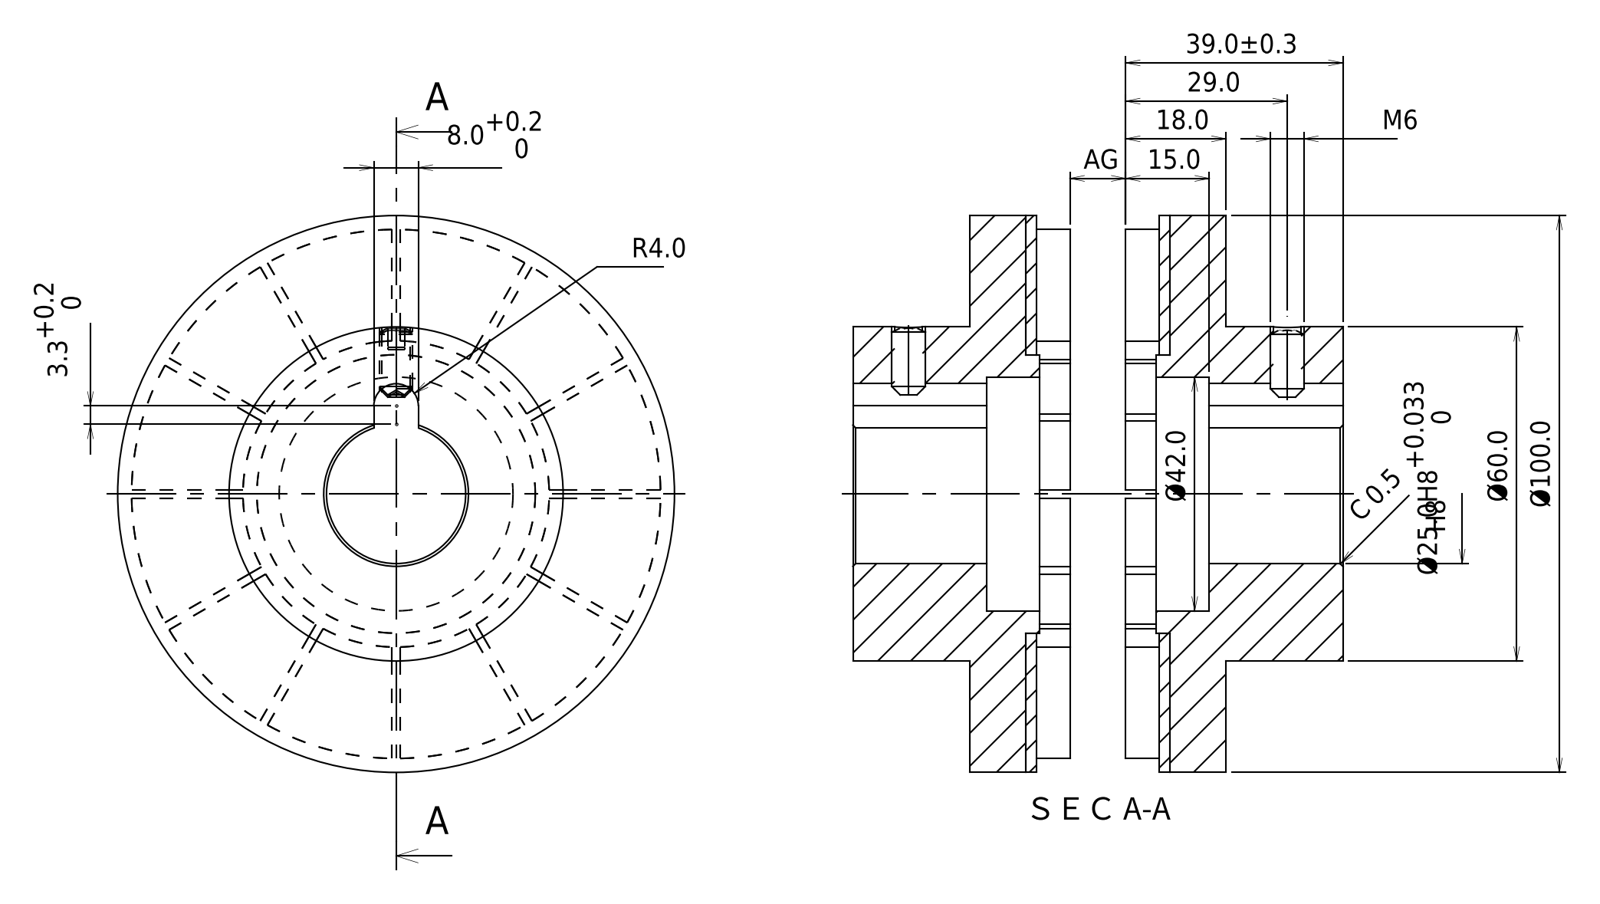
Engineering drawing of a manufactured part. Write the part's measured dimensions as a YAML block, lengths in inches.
step_written_by: "PSStep 10.0 (CONFIG_CONTROL_DESIGN)"
units: inches
bodies: {solids: 17, faces: 167, planar: 99, cylindrical: 61, other: 7}
overall_size: [3.937, 3.937, 1.535]
volume: 9.627
surface_area: 76.64
round_holes:
  - {diameter: 0.197, count: 1}
  - {diameter: 0.984, count: 1}
  - {diameter: 1.654, count: 1}
  - {diameter: 1.969, count: 1}
  - {diameter: 2.165, count: 1}
round_bosses_or_shafts:
  - {diameter: 3.937, count: 1}
  - {diameter: 3.74, count: 1}
  - {diameter: 2.362, count: 1}
  - {diameter: 0.236, count: 1}
partial_cylinders:
  - {radius: 0.157, count: 1}
face_to_face_distances: [0.394, 0.315, 0.709, 0.059, 1.535, 1.22, 0.827, 0.236, 0.079, 0.472]
